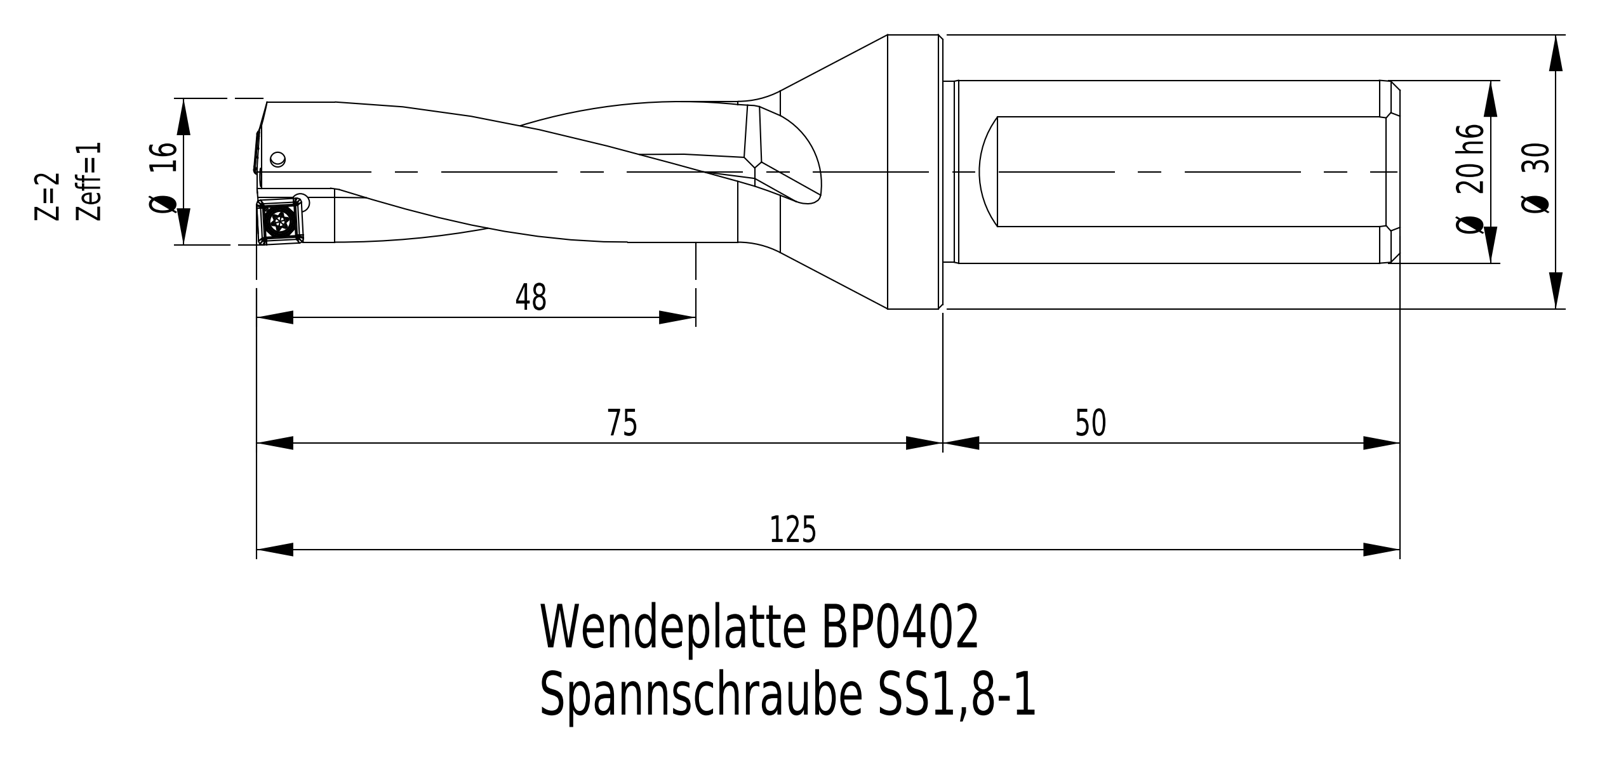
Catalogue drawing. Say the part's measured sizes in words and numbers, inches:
The part is named "BW-16-48-20-04". Its 3-D file was written by "SolidWorks 2015 (AUTOMOTIVE_DESIGN)". It is 1 solid with 45 faces: 7 planar, 14 cylindrical and 24 other. Overall it measures 4.919 by 1.181 by 1.181 inches. Its volume is 2.107 cubic inches and its surface area 14.19 square inches. Round holes: 1 of diameter 0.106, 1 of diameter 0.157. Round bosses or shafts: 1 of diameter 1.181, 1 of diameter 0.787, 1 of diameter 0.78, 1 of diameter 0.63, 1 of diameter 0.606. The main face-to-face distances are 1.969, 2.951, 4.919, 1.183, 0.197, 2.754, 4.722.
